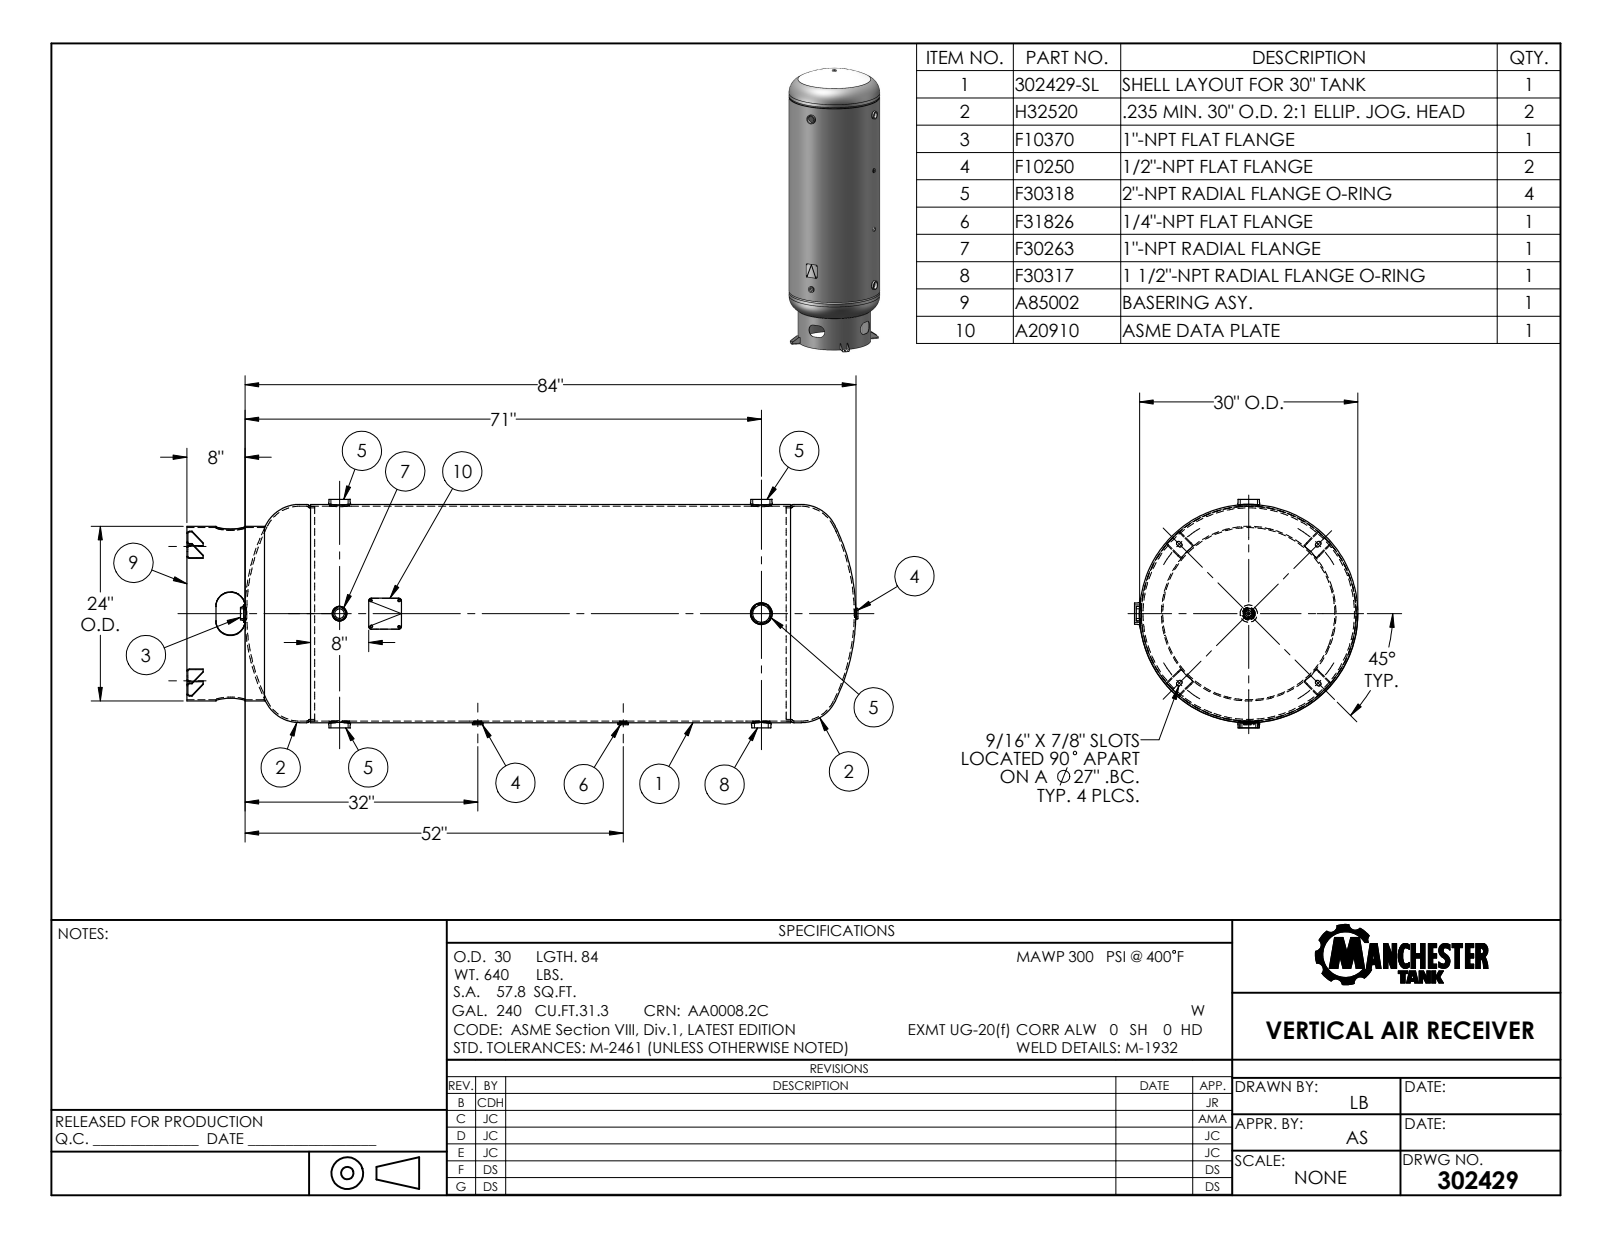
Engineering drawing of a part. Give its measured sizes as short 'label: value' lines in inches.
name: 302429
written by: SolidWorks 2011 (CONFIG_CONTROL_DESIGN)
unit: in
bodies: 0 solids, 289 faces (101 planar, 86 cylindrical, 102 other)
size: 92.432 × 31.674 × 30.812
holes: 3× ⌀2.375, 2× ⌀0.84, 1× ⌀0.54, 1× ⌀1, 1× ⌀1.315, 1× ⌀1.315, 1× ⌀1.9, 1× ⌀23.638, 1× ⌀29.374
bosses: 3× ⌀3.625, 2× ⌀2.375, 2× ⌀1.813, 1× ⌀30, 1× ⌀29.313, 1× ⌀24, 1× ⌀2.688, 1× ⌀1.75
rounds: 8× R0.25, 8× R0.384, 7× R0.281, 1× R15.06
face distances: 16.838, 66.25, 83.089, 0.134, 2.383, 82.954, 16.704, 0.134, 2.517, 2.25
hole spacings: 19, 39, 58, 20
